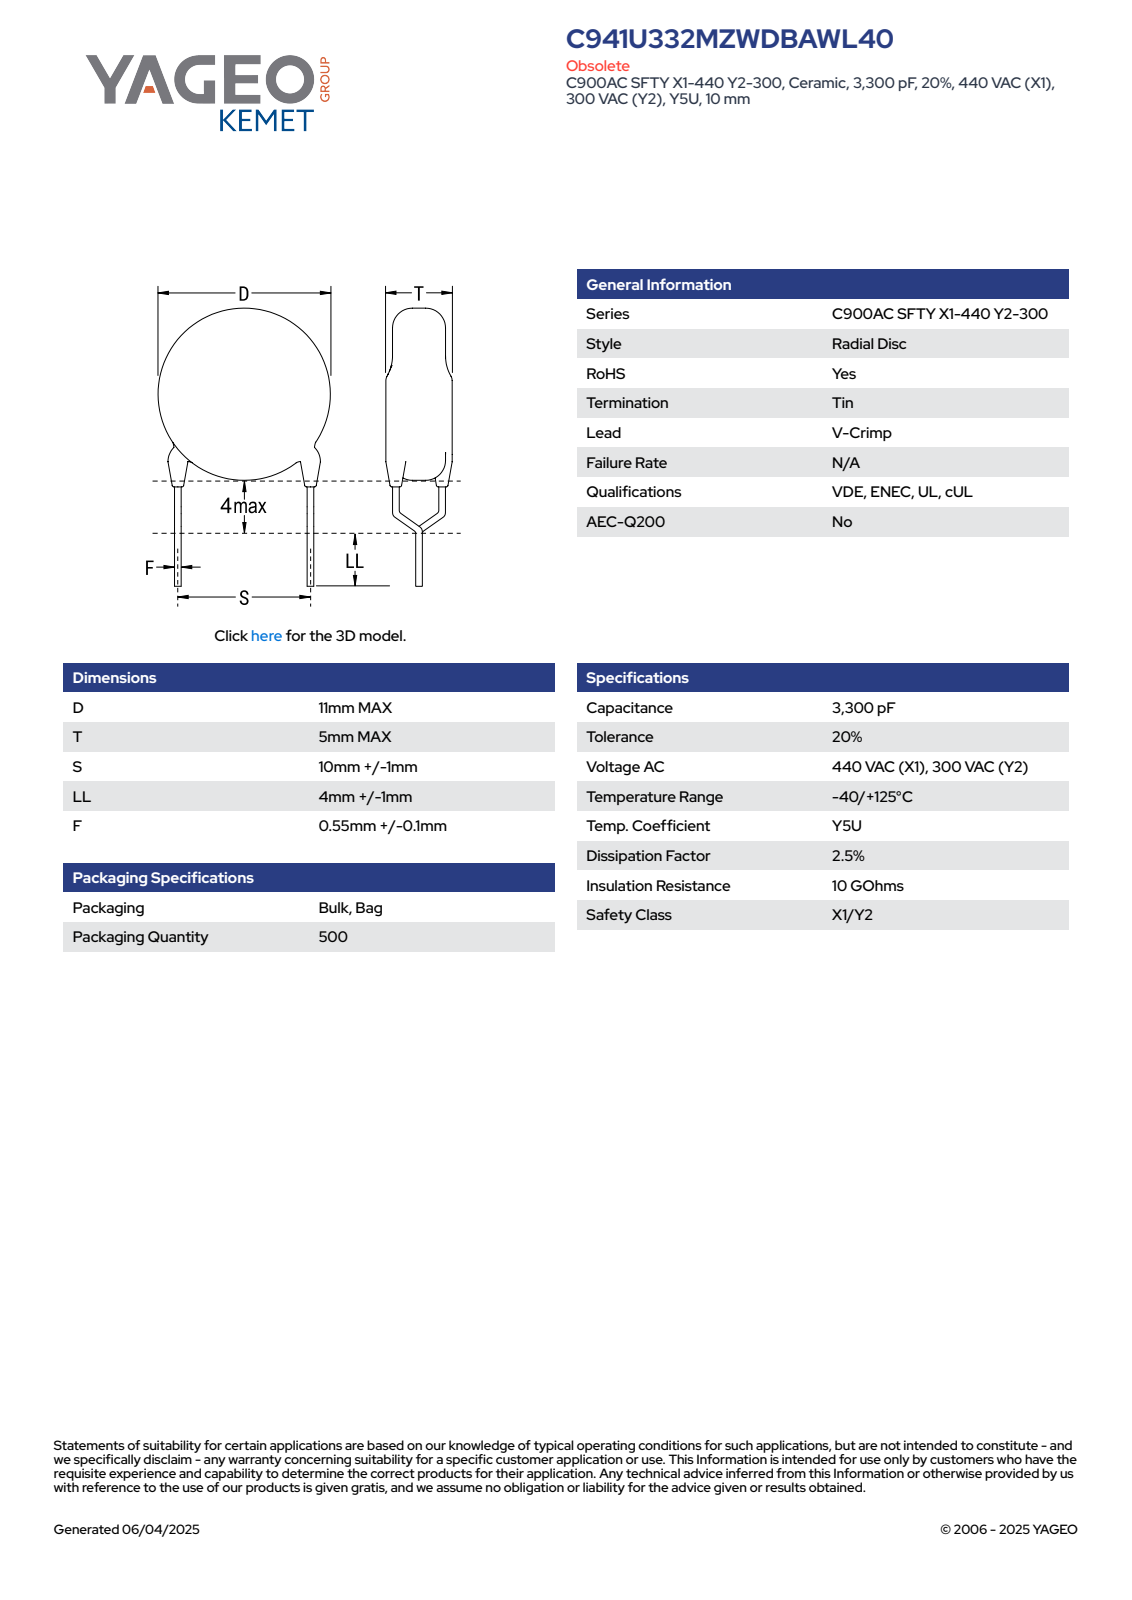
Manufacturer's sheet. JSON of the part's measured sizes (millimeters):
{"part_name": "CCD_VCC900_D11T5S10LL5F0.65", "step_written_by": "SolidWorks 2014 (AUTOMOTIVE_DESIGN)", "units": "millimeters", "bodies": {"solids": 5, "faces": 93, "planar": 65, "cylindrical": 16, "other": 12}, "overall_size": [19.8, 11, 5], "volume_mm3": 471, "surface_area_mm2": 395, "round_bosses_or_shafts": [[0.65, 6], [11, 1]], "face_to_face_distances": [5, 7.9, 15.01, 7.11, 13.58, 5.68, 1.43, 0.39, 0.35, 5.84]}
